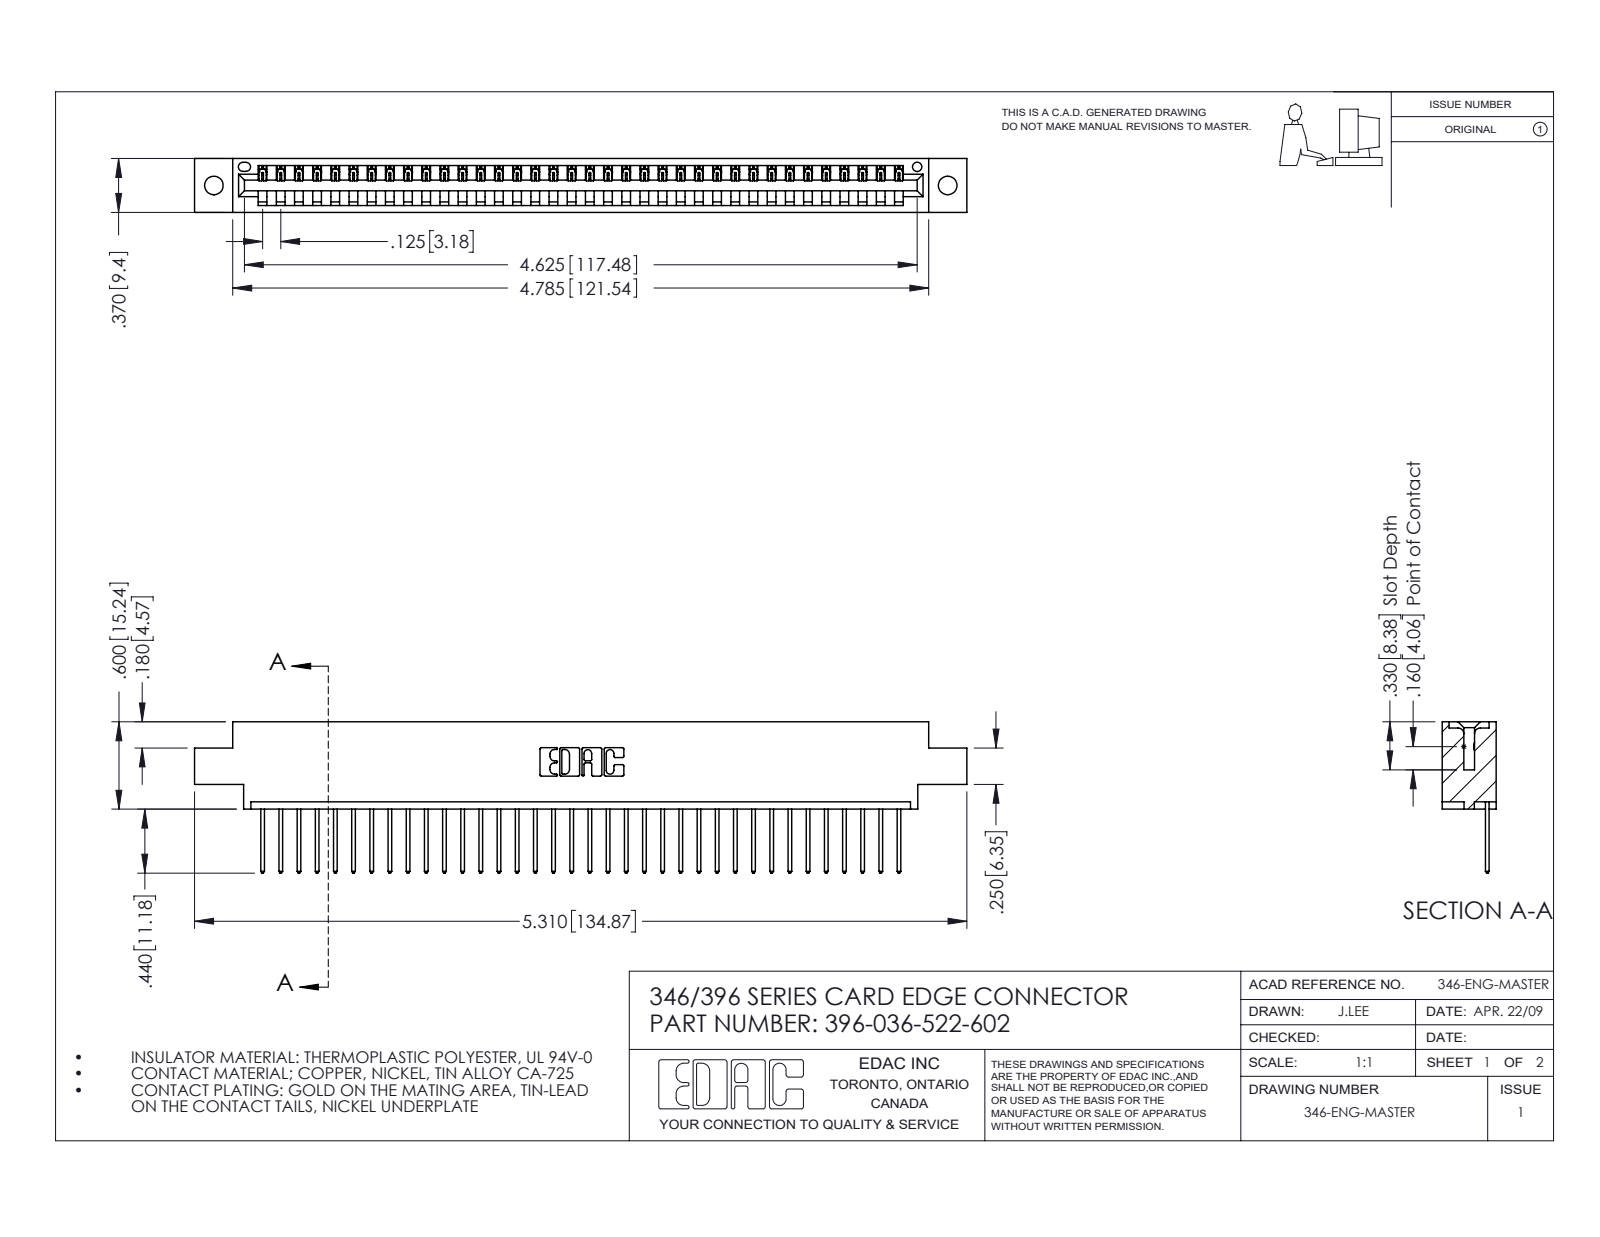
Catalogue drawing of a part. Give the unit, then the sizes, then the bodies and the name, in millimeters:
Units: millimetres
Overall size (bounding box): 134.9 × 26.4 × 9.4
Round holes (diameter × count): ⌀3.3 ×2, ⌀1.6 ×1
Partial cylindrical surfaces — rounded edges, fillets, slot ends (radius × count): R0.2 ×72, R0.3 ×72, R0.3 ×22, R0.2 ×6, R0.8 ×6, R0.7 ×3, R0.8 ×2, R1 ×2
Main face-to-face distances: 1.2, 8.2, 9.4, 6.4, 1.8, 7.6, 0.6, 3.8, 5.6, 2.5
Hole centre spacings: 6.2, 122.8, 128.1
Volume: 12 700 mm³ · Surface area: 15 810 mm²
Bodies: 37 solids, 2214 faces (1520 planar, 694 cylindrical, 0 other)
Part name (STEP PRODUCT): 345-292-001_345-293-122; 396-036-522-602; 346 Part_0.170 Offset - 0.128 Dia
STEP written by: SolidWorks 2016 (CONFIG_CONTROL_DESIGN)
